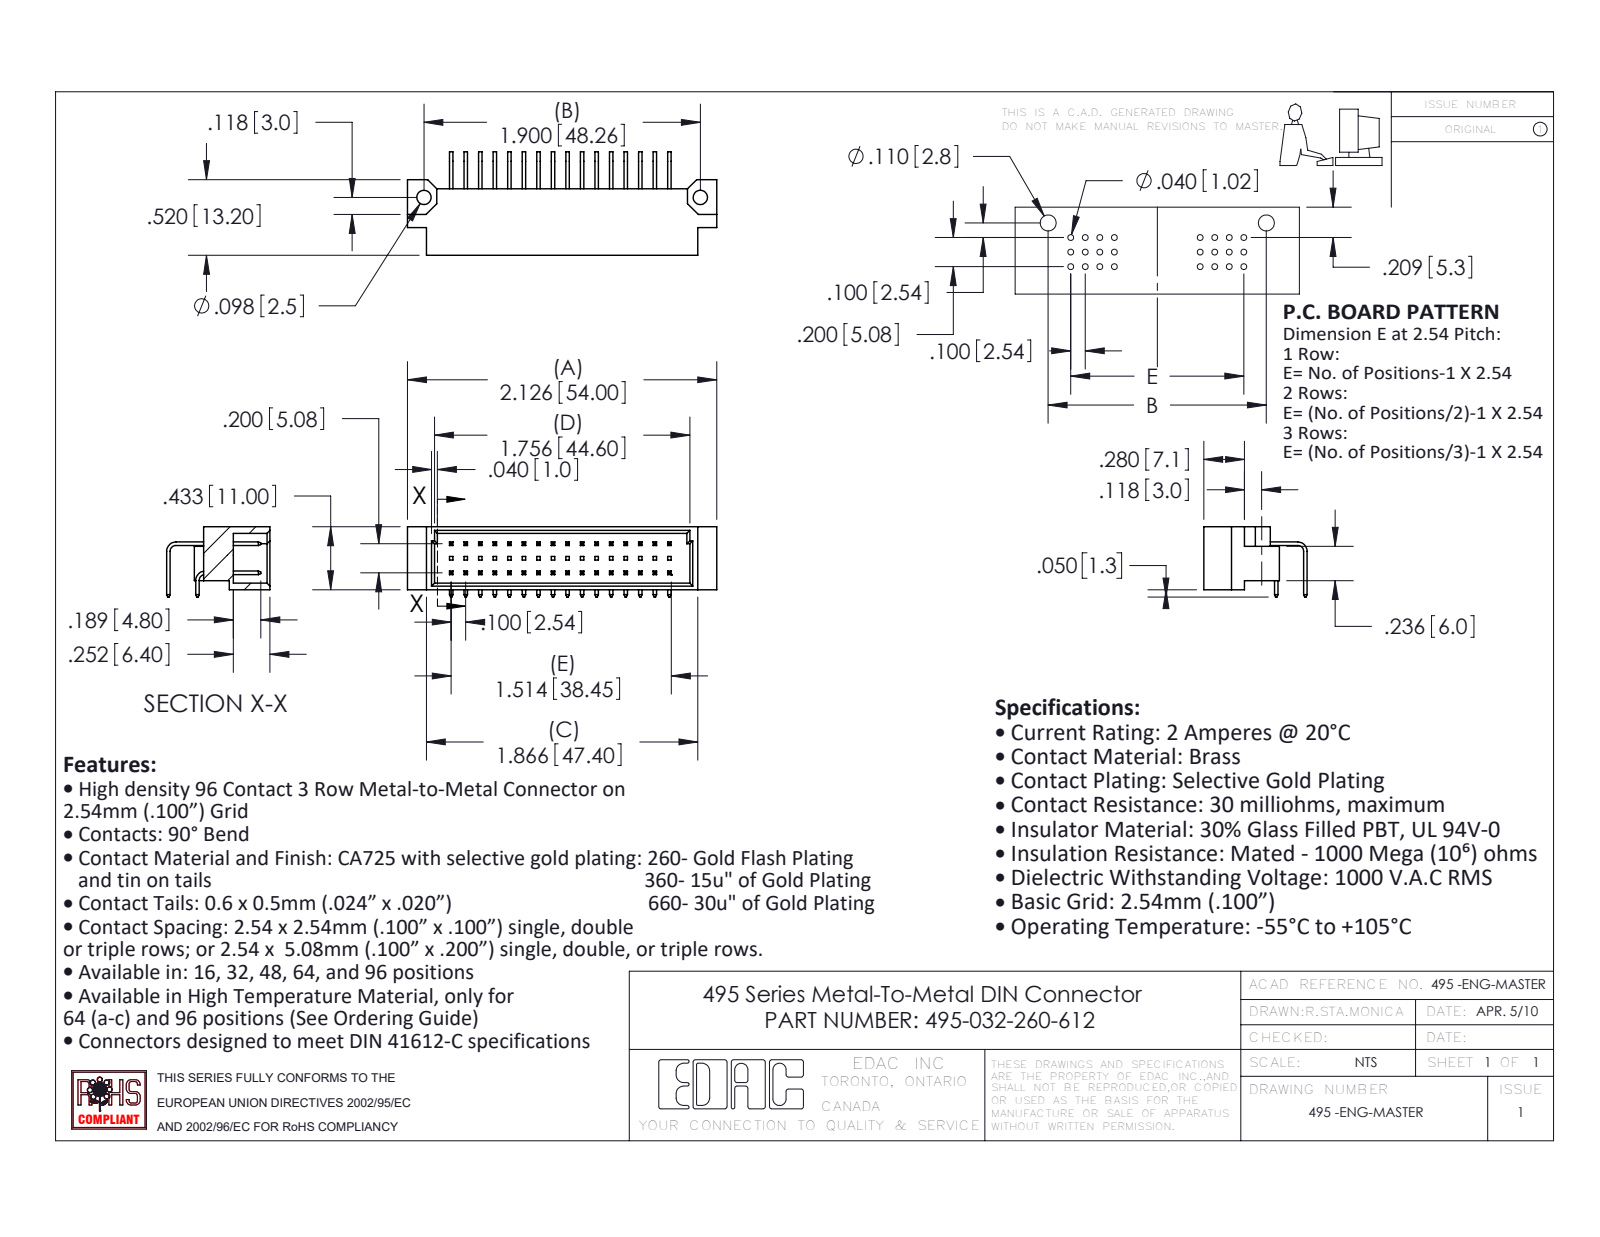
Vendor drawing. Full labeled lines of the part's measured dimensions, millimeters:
Part name (STEP PRODUCT): 495-290-3; 495 Part_48; 495-290-1; 495-032-260-612
STEP written by: SolidWorks 2020 (AUTOMOTIVE_DESIGN)
Units: millimetres
Bodies: 33 solids, 818 faces (750 planar, 68 cylindrical, 0 other)
Overall size (bounding box): 54 × 18.05 × 12.27
Volume: 3 680 mm³ · Surface area: 5 496 mm²
Round holes (diameter × count): ⌀2.49 ×2
Partial cylindrical surfaces — rounded edges, fillets, slot ends (radius × count): R1.02 ×2, R1.65 ×2
Main face-to-face distances: 5.08, 2.54, 1.14, 9.86, 0.61, 5.2, 11, 7.62, 1.6, 10.16
Hole centre spacings: 48.26
